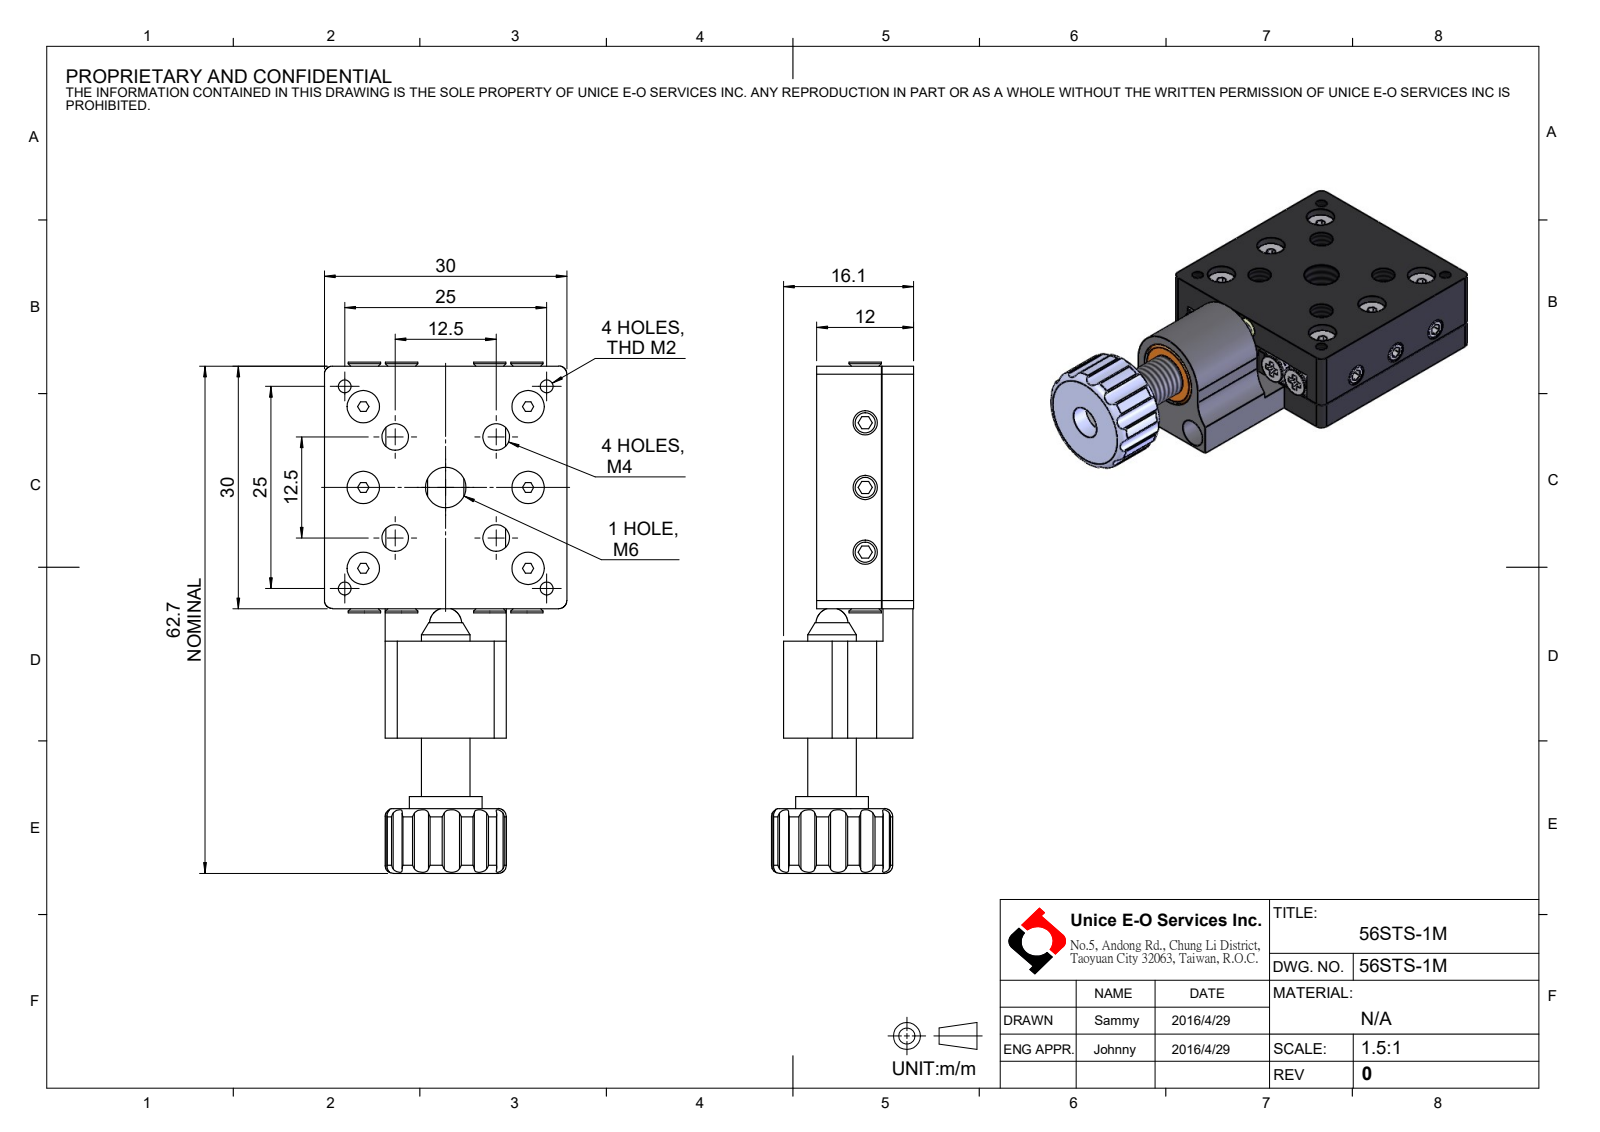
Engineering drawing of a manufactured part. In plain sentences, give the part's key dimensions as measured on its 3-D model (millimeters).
The part is named "56STS-1M". Its 3-D file was written by "SolidWorks 2016 (CONFIG_CONTROL_DESIGN)". It is 38 solids with 837 faces: 441 planar, 318 cylindrical and 78 other. Overall it measures 63.23 by 30 by 17.59 millimeters. Its volume is 13 472 cubic millimeters and its surface area 14 554 square millimeters. Round holes: 24 of diameter 1.6, 15 of diameter 4, 10 of diameter 2.5, 6 of diameter 2.4, 4 of diameter 3.3, 2 of diameter 2.1, 1 of diameter 3, 1 of diameter 4.7, 1 of diameter 5, 1 of diameter 5.9, 1 of diameter 6, 1 of diameter 9.5. Round bosses or shafts: 18 of diameter 2, 4 of diameter 4, 4 of diameter 3, 1 of diameter 9. Partial cylindrical surfaces (rounded edges, fillets, slot ends): 24 of radius 0.3, 12 of radius 1.5, 4 of radius 1, 2 of radius 5, 1 of radius 6, 1 of radius 7.5. The main face-to-face distances are 4, 8, 3.9, 8.1, 4.1, 12, 3, 15.5, 30, 4.2. The hole center spacings are 10, 8.84, 11.14, 15.5, 18.45, 19.76, 4.9, 17.68.
